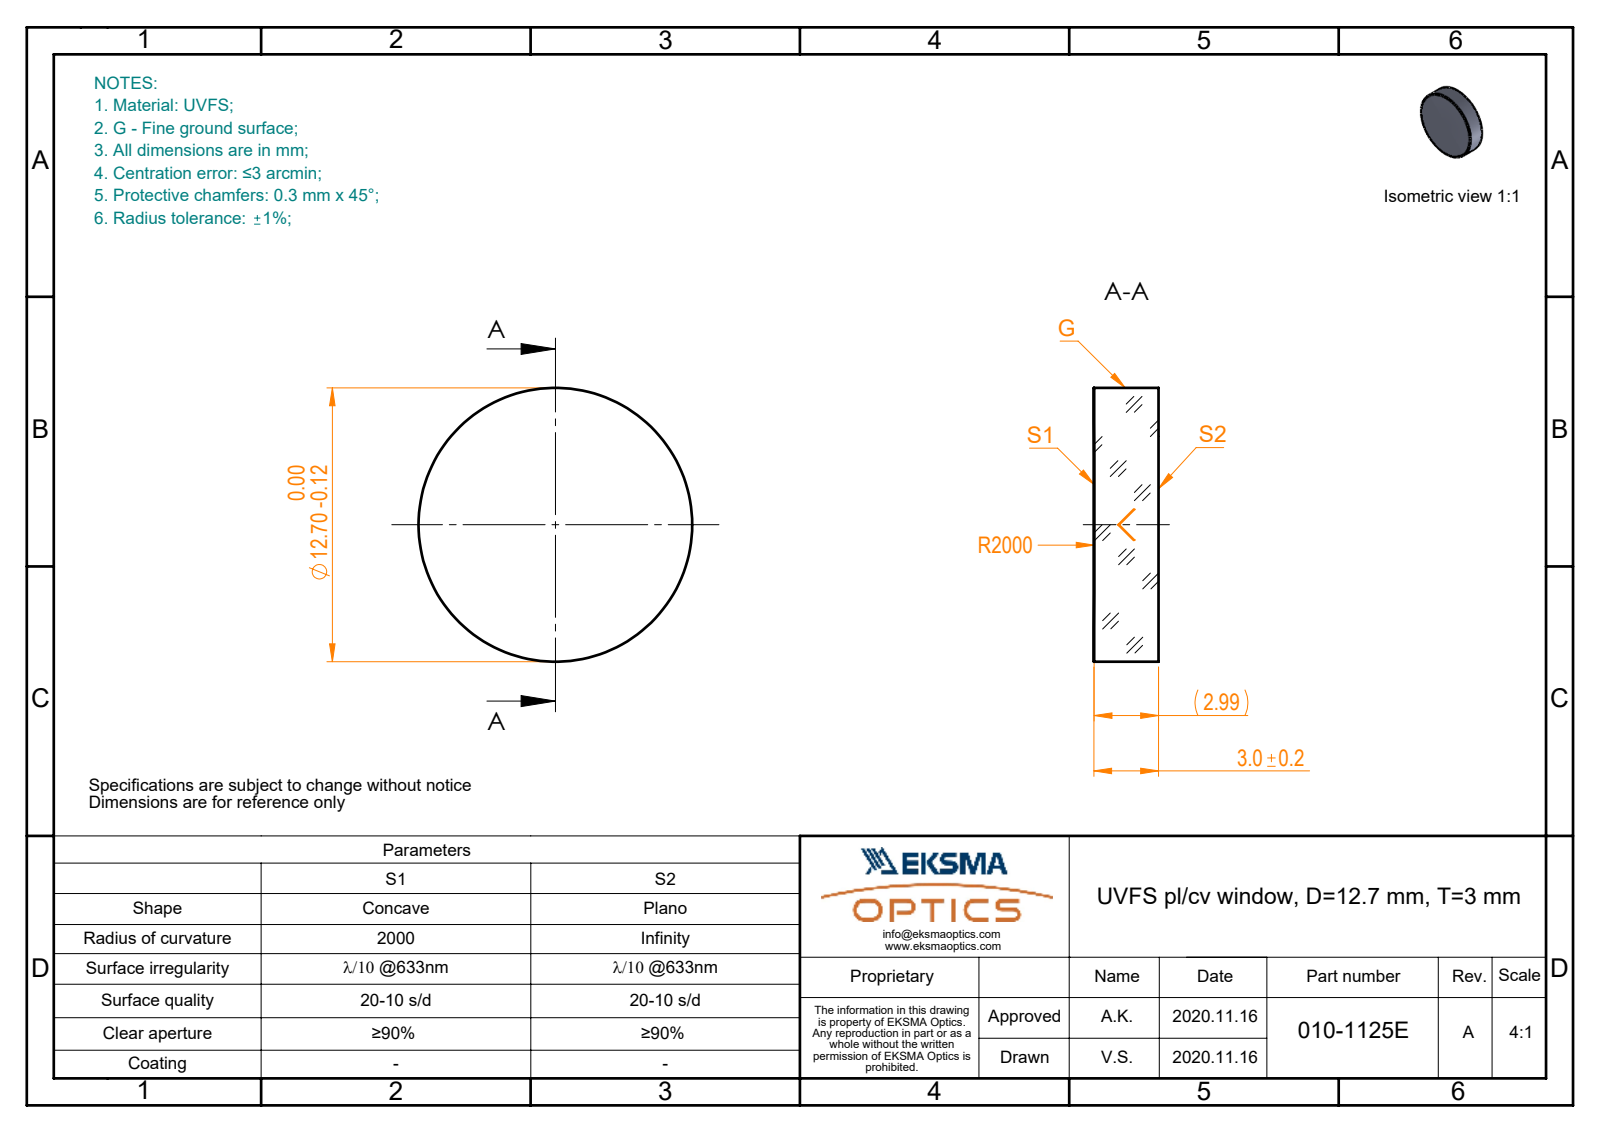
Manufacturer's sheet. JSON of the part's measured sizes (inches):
{"part_name": "010-1125E_UVFS_PCV_window", "step_written_by": "SolidWorks 2019 (CONFIG_CONTROL_DESIGN)", "units": "inches", "bodies": {"solids": 1, "faces": 5, "planar": 1, "cylindrical": 2, "other": 2}, "overall_size": [0.5, 0.5, 0.118], "volume_in3": 0.023, "surface_area_in2": 0.578, "round_bosses_or_shafts": [[0.5, 1]]}
